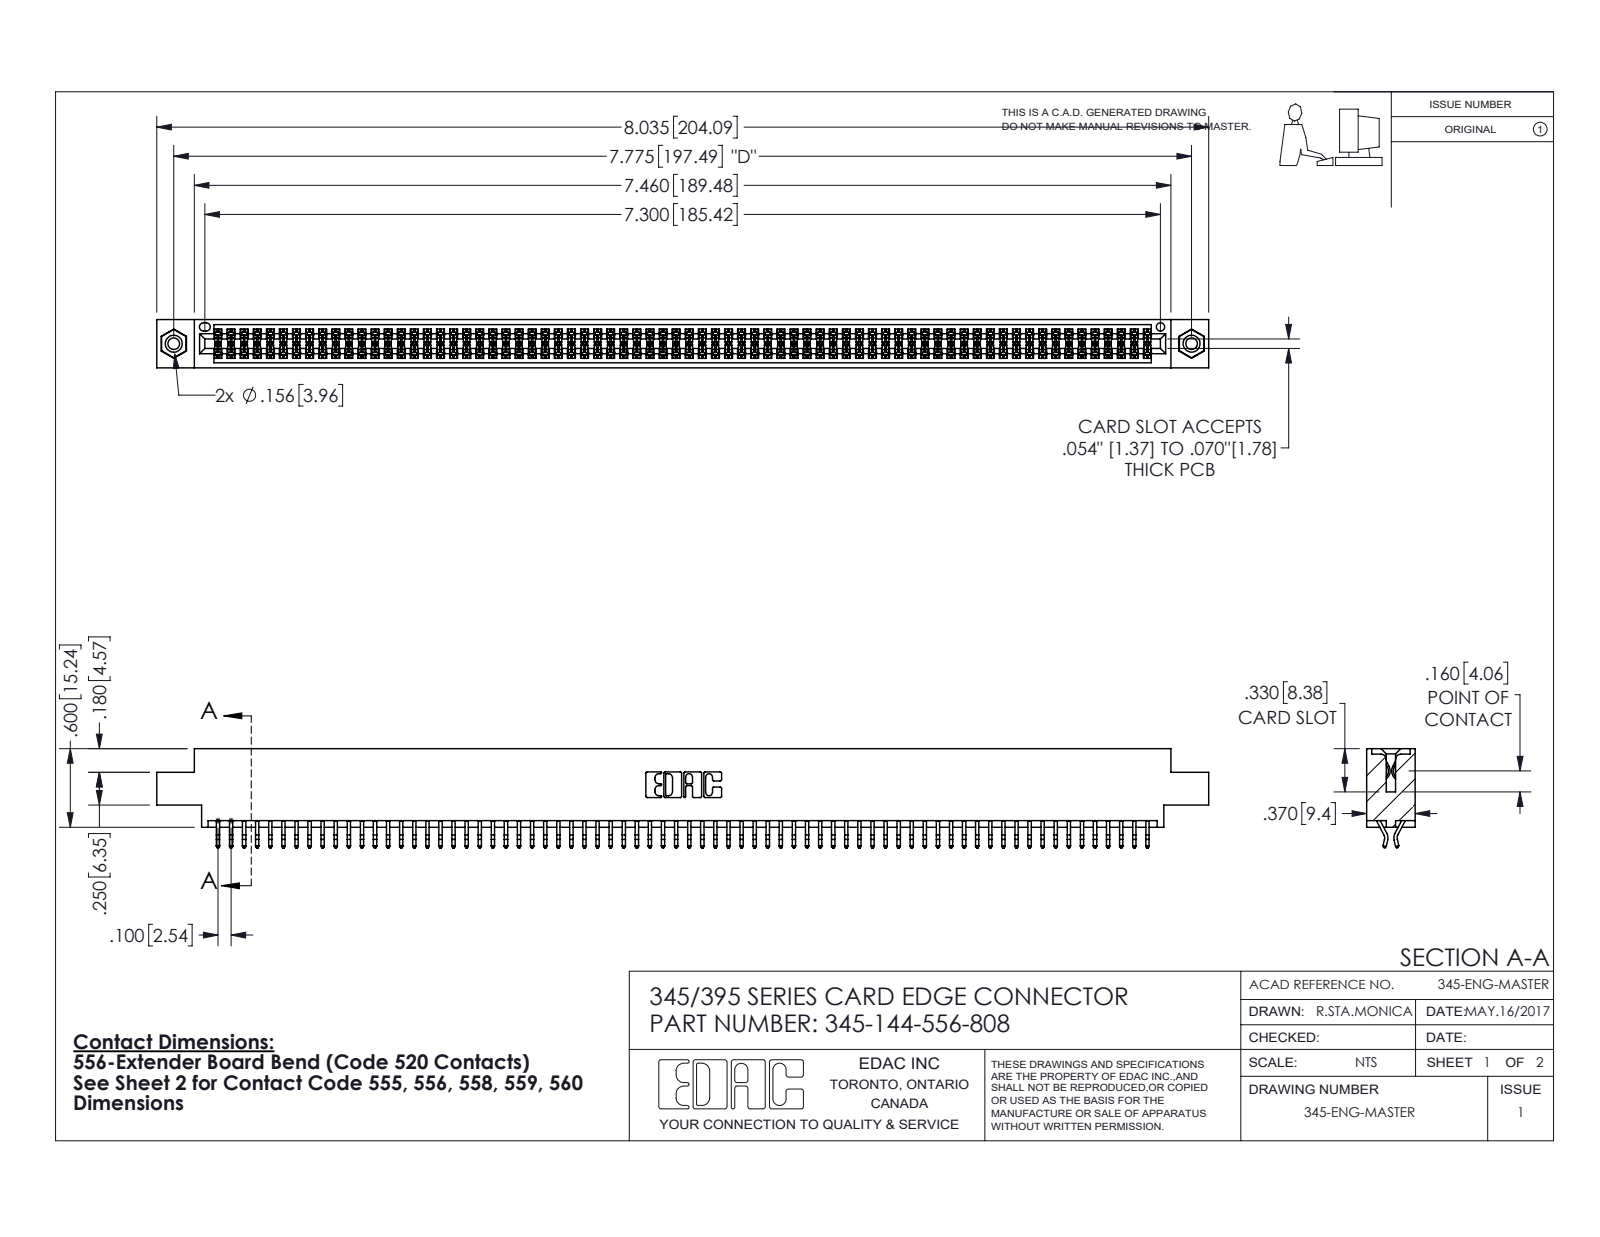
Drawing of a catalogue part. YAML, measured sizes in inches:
part_name: "345-292-001_556 Tail; 345-250-001_345-250-003-102; 345-144-556-808; 345 Part_0.170 Offset - 0.156 Dia-TI"
step_written_by: "SolidWorks 2016 (CONFIG_CONTROL_DESIGN)"
units: inches
bodies: {solids: 147, faces: 8254, planar: 5444, cylindrical: 2794, other: 16}
overall_size: [8.035, 0.757, 0.37]
volume: 1.219
surface_area: 46.72
round_holes:
  - {diameter: 0.089, count: 2}
  - {diameter: 0.125, count: 2}
  - {diameter: 0.156, count: 2}
  - {diameter: 0.064, count: 1}
round_bosses_or_shafts:
  - {diameter: 0.155, count: 2}
partial_cylinders:
  - {radius: 0.006, count: 216}
  - {radius: 0.01, count: 22}
  - {radius: 0.007, count: 6}
  - {radius: 0.031, count: 6}
  - {radius: 0.026, count: 3}
  - {radius: 0.01, count: 2}
  - {radius: 0.014, count: 2}
  - {radius: 0.019, count: 2}
face_to_face_distances: [0.072, 0.298, 0.37, 0.2, 0.025, 0.098, 0.272, 0.225, 0.175, 0.149]
hole_center_spacings: [0.27, 7.539, 7.775]
